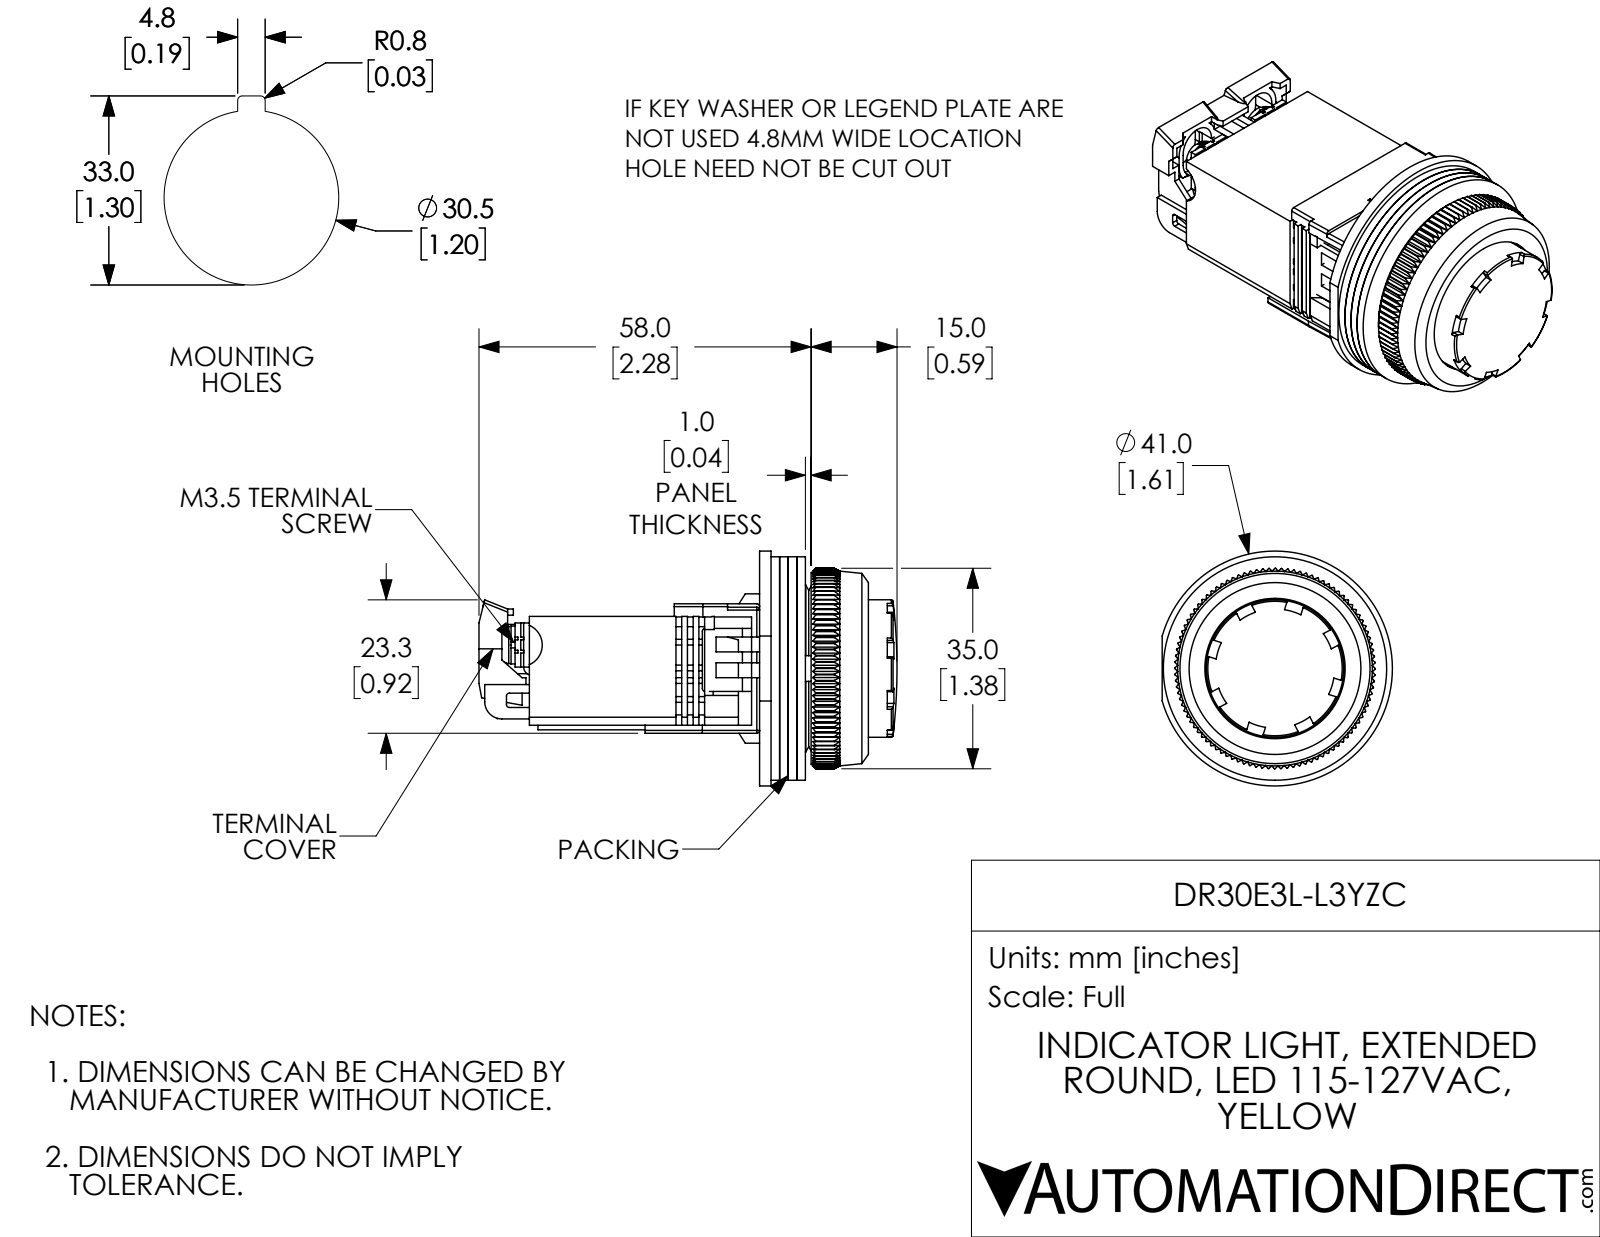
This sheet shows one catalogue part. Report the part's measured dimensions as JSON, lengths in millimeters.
{"part_name": "DR30E3L-L3YZC", "step_written_by": "SolidWorks 2017 (AUTOMOTIVE_DESIGN)", "units": "millimeters", "bodies": {"solids": 19, "faces": 1662, "planar": 1058, "cylindrical": 340, "other": 264}, "overall_size": [73, 41, 40.2], "volume_mm3": 37990, "surface_area_mm2": 34230, "round_holes": [[3, 2], [3.5, 2], [3.6, 2], [11.8, 1], [14.3, 1], [18.3, 1], [20, 1], [22, 1], [24.5, 1], [28.5, 1], [29.8, 1], [30, 1]], "round_bosses_or_shafts": [[6.6, 2], [1.6, 2], [41, 1], [39, 1], [29.5, 1], [24, 1], [21.8, 1], [20.8, 1]], "partial_cylinders_radius": [[0.5, 24], [0.3, 16], [1.5, 9], [3.5, 2], [4.5, 2], [0.4, 1], [1.4, 1], [3, 1]], "face_to_face_distances": [1.5, 3, 1, 4.5, 5, 2, 6.5, 8, 19, 3.5], "hole_center_spacings": [8.5, 0.5, 8.2, 14.8, 14.8]}
